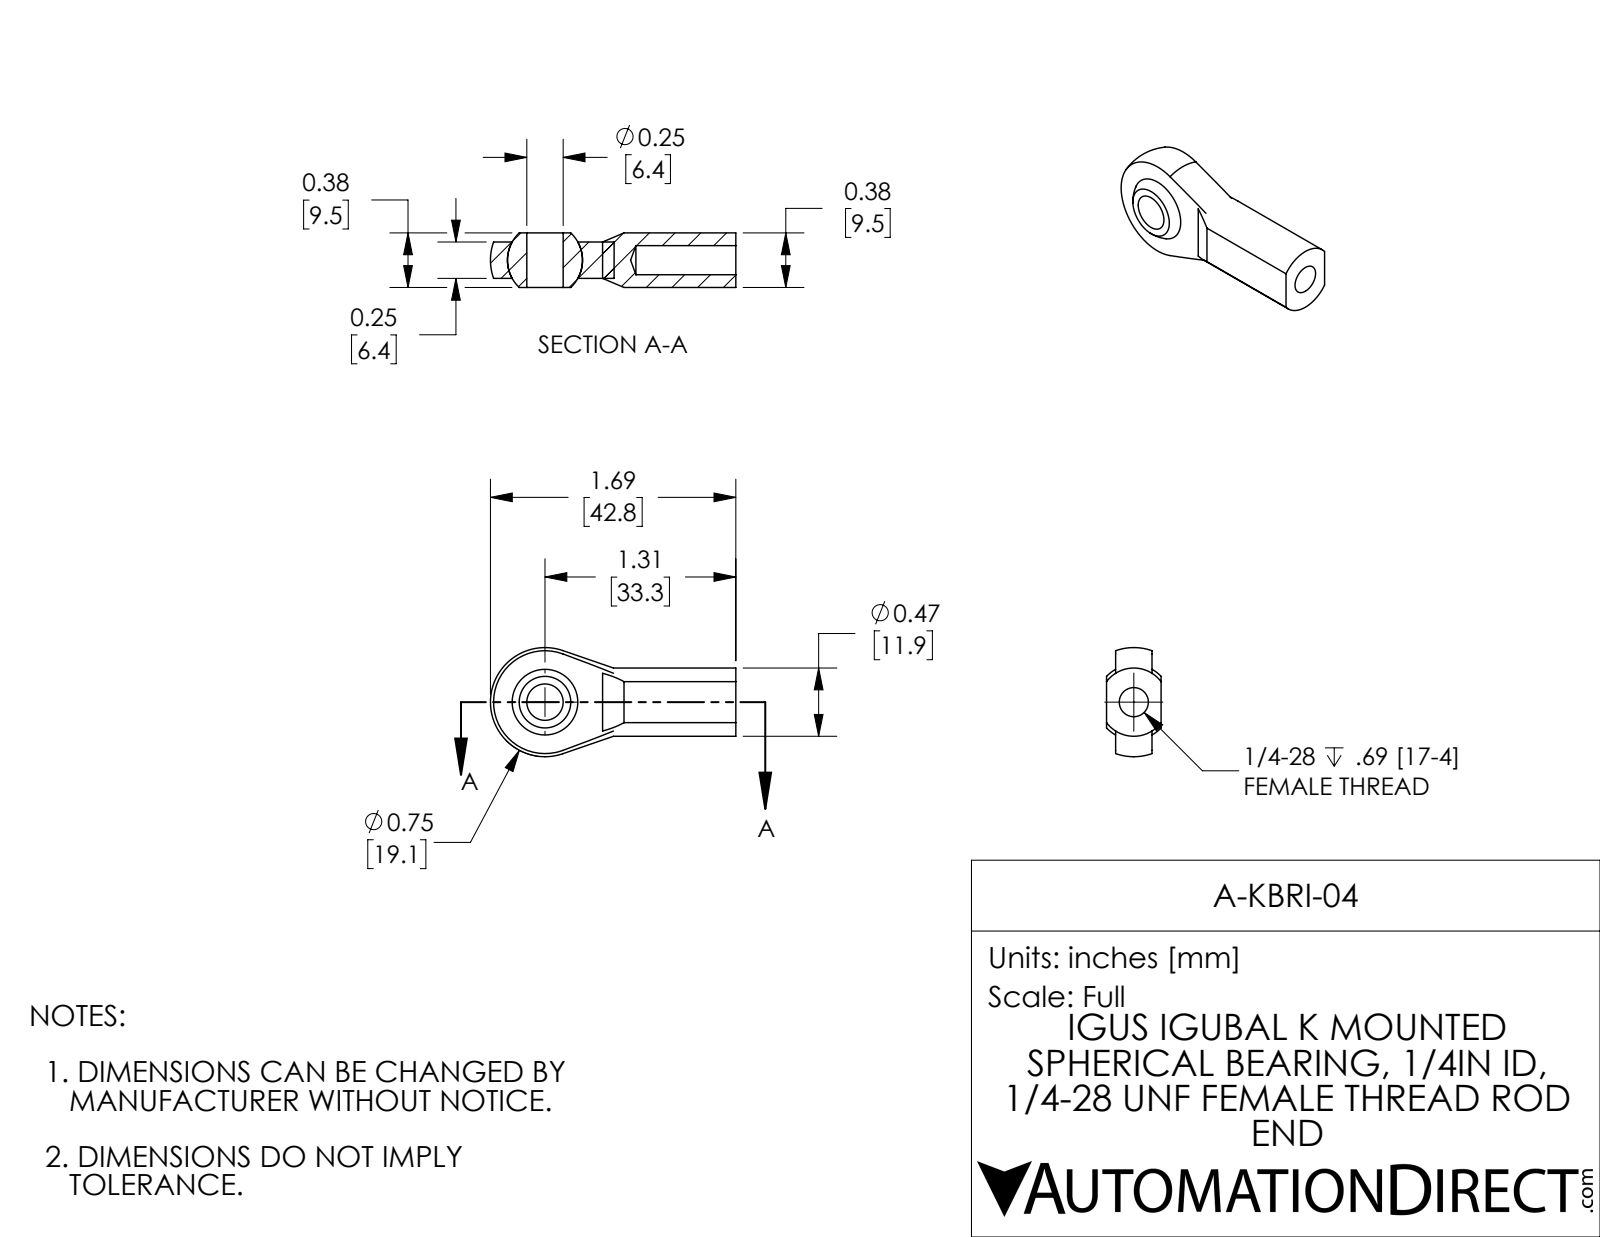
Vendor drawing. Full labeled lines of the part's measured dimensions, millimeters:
Part name (STEP PRODUCT): A-KBRI-04
STEP written by: SolidWorks 2017 (AUTOMOTIVE_DESIGN)
Units: millimetres
Bodies: 3 solids, 30 faces (11 planar, 7 cylindrical, 12 other)
Overall size (bounding box): 42.8 × 19.1 × 9.5
Volume: 3 930 mm³ · Surface area: 3 031 mm²
Round holes (diameter × count): ⌀5.1 ×1, ⌀6.4 ×1
Partial cylindrical surfaces — rounded edges, fillets, slot ends (radius × count): R5.9 ×1
Main face-to-face distances: 1.6, 7.9, 6.4, 9.5, 23.3, 21.3, 2
